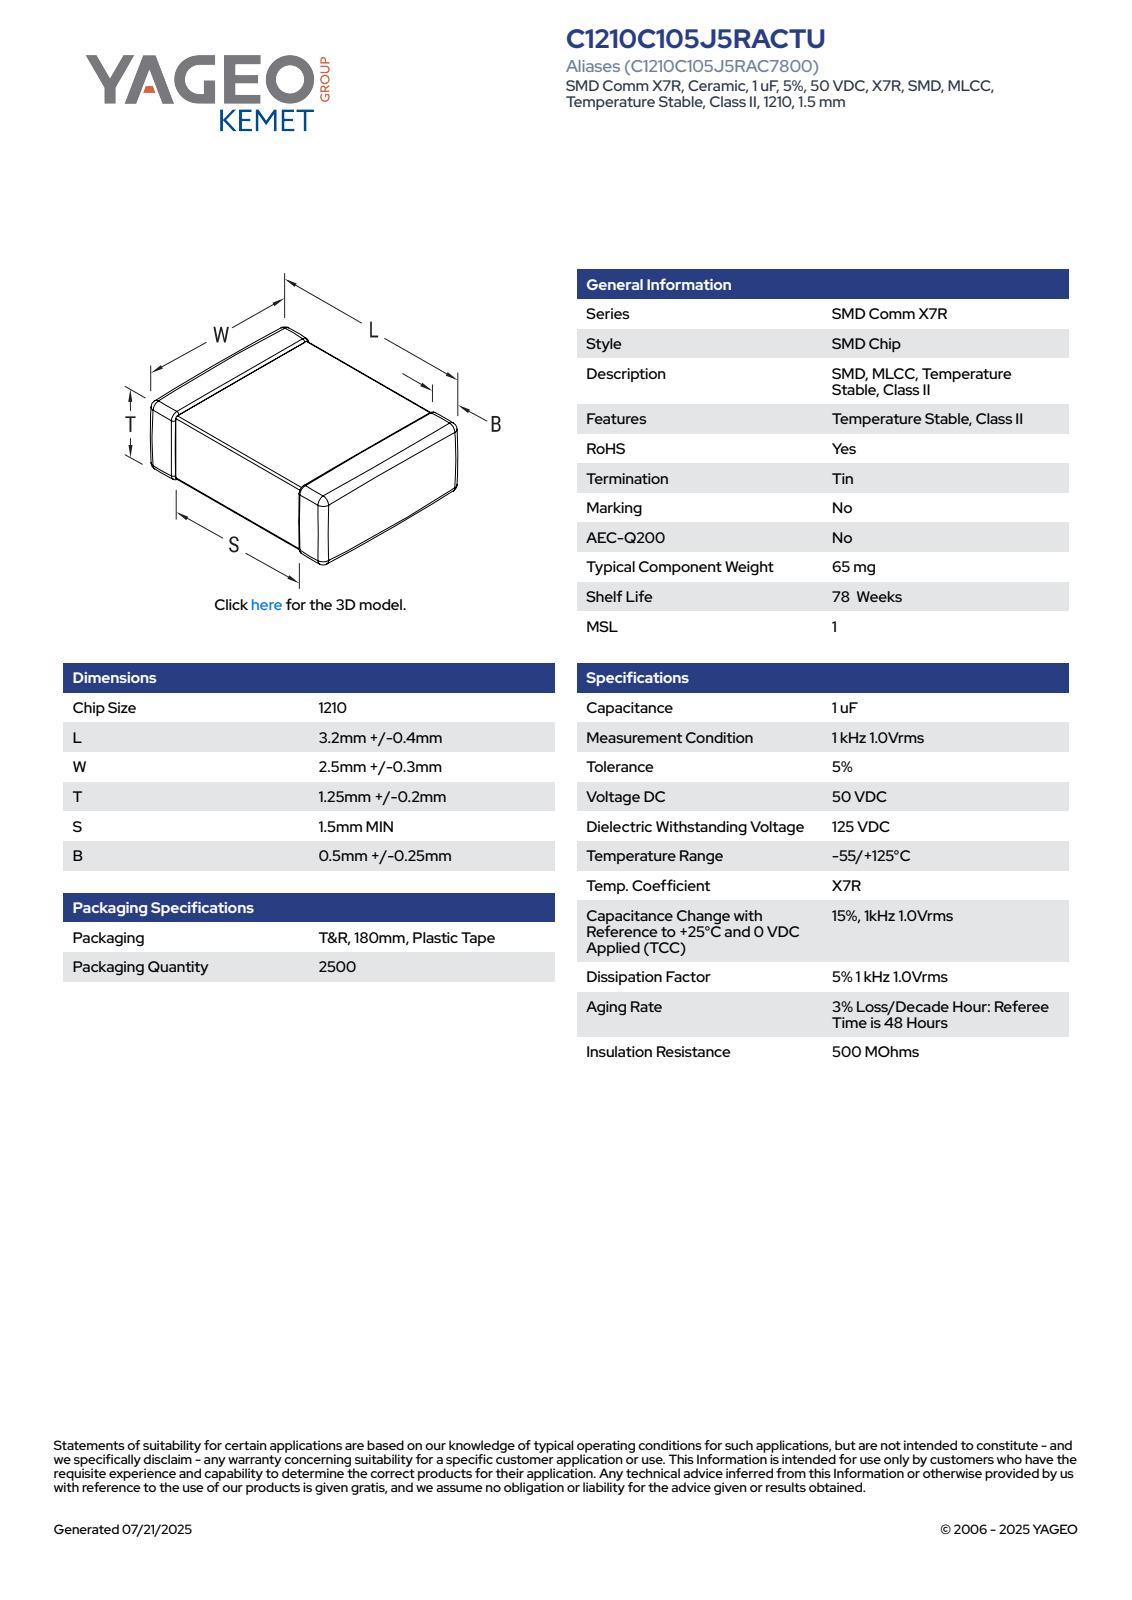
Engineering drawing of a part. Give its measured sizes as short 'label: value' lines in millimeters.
name: CCS_CCSTD_1210_L3.6W2.8T1.45B0.5
written by: SolidWorks 2021 (AUTOMOTIVE_DESIGN)
unit: mm
bodies: 4 solids, 125 faces (71 planar, 38 cylindrical, 16 other)
size: 3.6 × 2.8 × 1.45
volume: 14 mm³; area: 39 mm²
face distances: 1.39, 1.33, 3.6, 1.45, 2.74, 2.68, 2.8, 1.4, 1.34, 1.53
